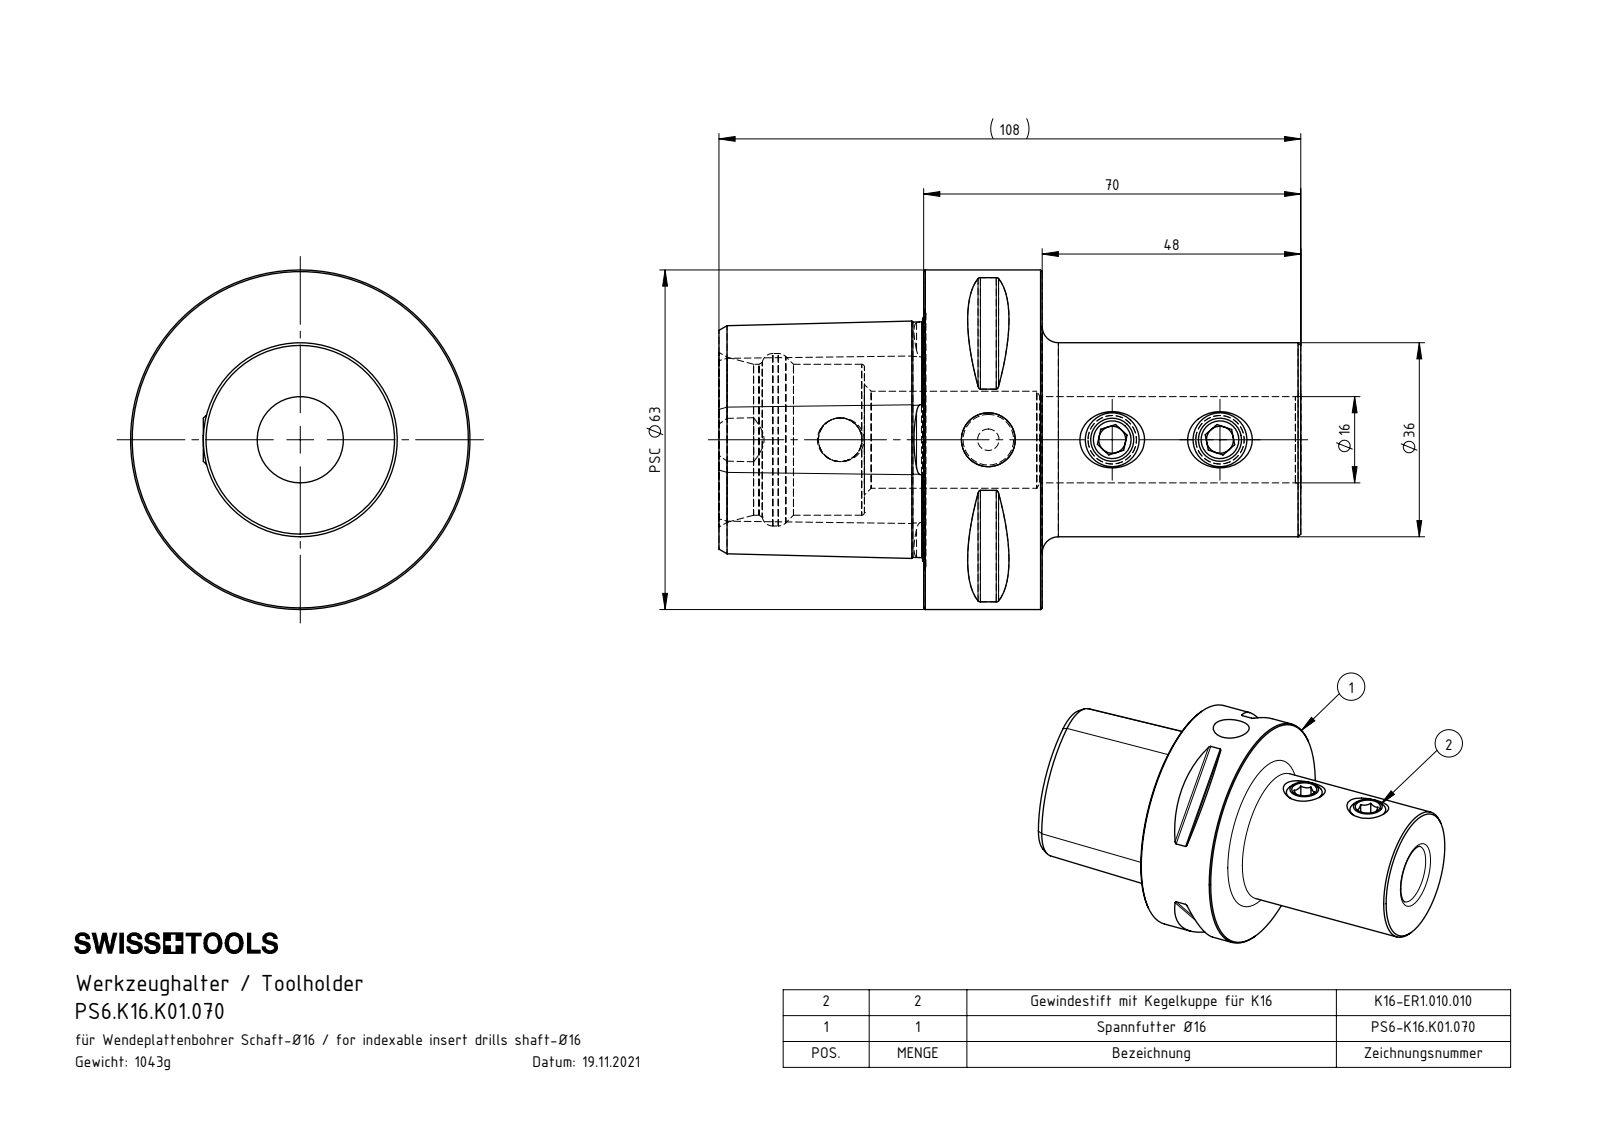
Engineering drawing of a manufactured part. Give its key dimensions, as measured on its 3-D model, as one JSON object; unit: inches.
{"part_name": "PS6-K16.K01.070_A; K16-ER1.010.010_A_PreviewCfg; PS6.K16.K01.070", "step_written_by": "SolidWorks 2017 (AUTOMOTIVE_DESIGN)", "units": "inches", "bodies": {"solids": 3, "faces": 140, "planar": 49, "cylindrical": 26, "other": 65}, "overall_size": [4.252, 2.48, 2.48], "volume_in3": 8.108, "surface_area_in2": 45.24, "round_holes": [[0.197, 2], [0.354, 2], [0.319, 1], [0.394, 1], [0.63, 1], [0.709, 1], [1.102, 1], [1.26, 1]], "round_bosses_or_shafts": [[0.394, 2], [2.48, 1], [1.417, 1]], "partial_cylinders_radius": [[0.02, 8], [0.236, 1]], "face_to_face_distances": [0.866, 2.756, 1.89, 1.496, 2.362, 4.252, 0.98, 1.063, 0.433, 1.299], "hole_center_spacings": [0.787, 0.906, 1.083, 1.693, 1.988, 2.776]}
